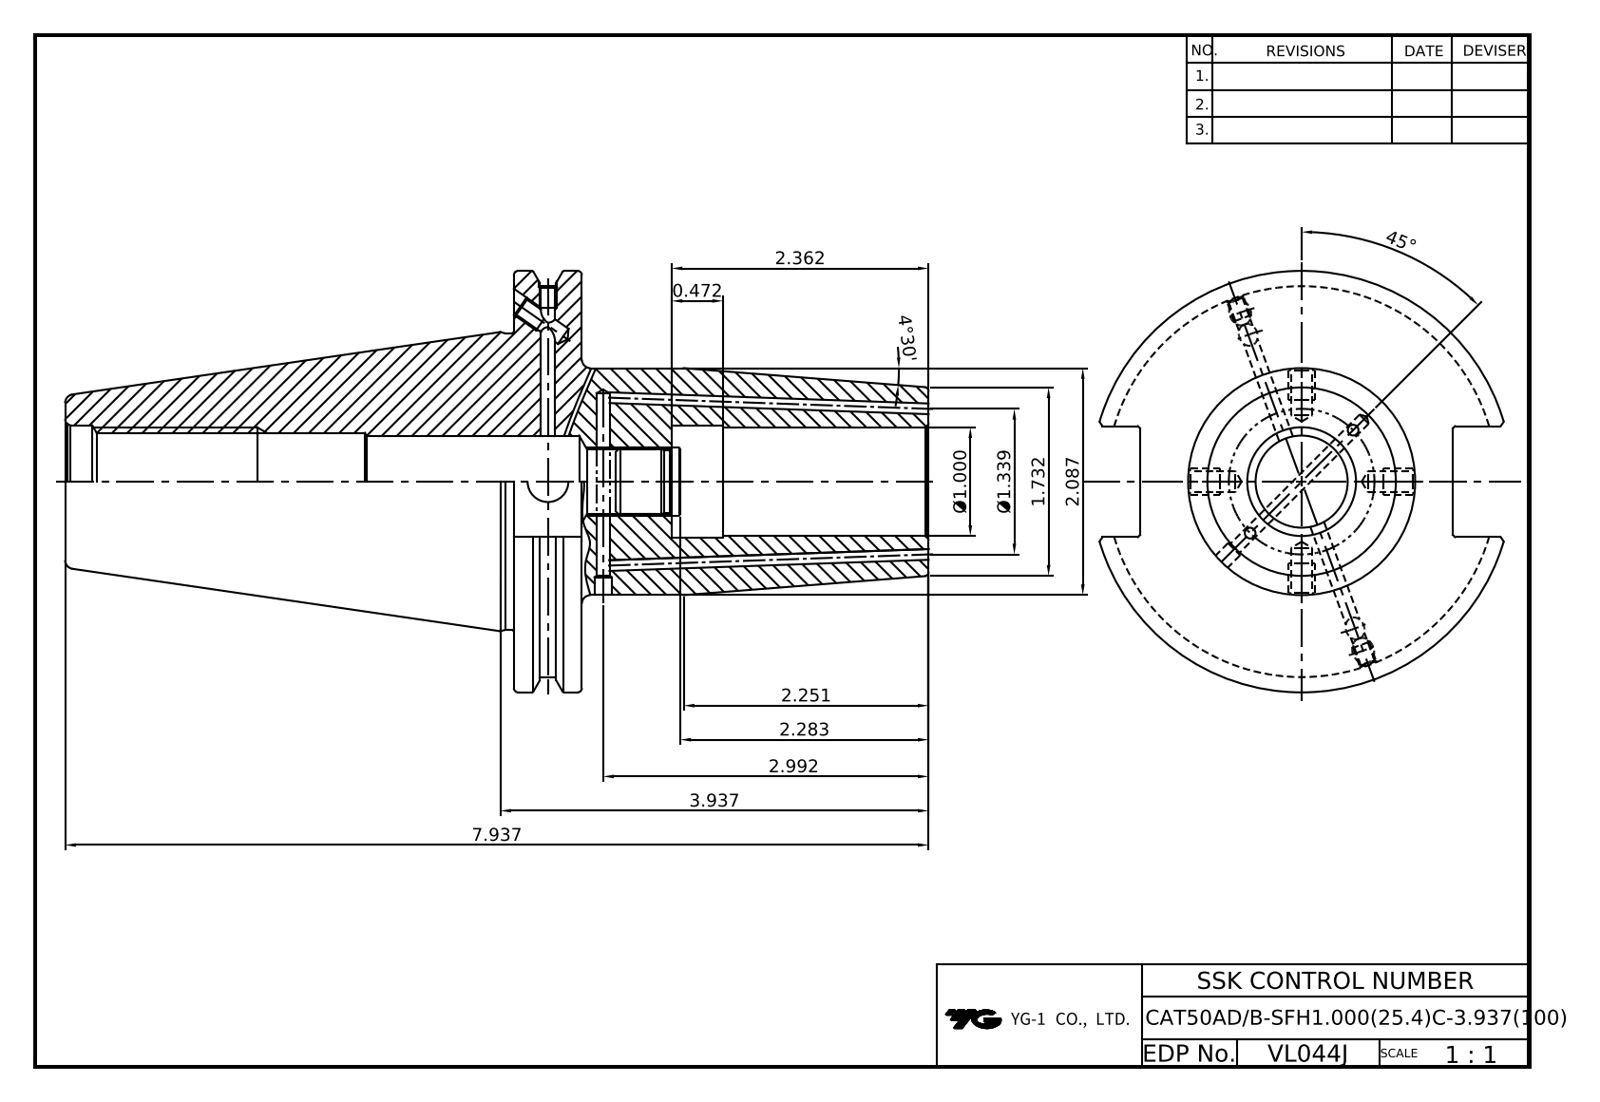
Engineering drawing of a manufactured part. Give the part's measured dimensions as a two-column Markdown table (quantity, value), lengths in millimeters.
| quantity | value |
| --- | --- |
| part name | LO-CAT50ADB-SFH25.4C-100 |
| STEP written by | Autodesk Inventor 2025 (AUTOMOTIVE_DESIGN) |
| units | millimeters |
| bodies | 1 solid, 88 faces (37 planar, 28 cylindrical, 23 other) |
| overall size | 201.6 × 98.42 × 94.69 |
| volume | 442 085 mm³ |
| surface area | 63 491 mm² |
| round holes (diameter × count) | 2.5 × 2, 3.24 × 2, 4.13 × 2, 4.2 × 2, 5 × 2, 9.53 × 1, 14.92 × 1, 21.97 × 1, 25.4 × 1, 26.2 × 1, 26.6 × 1 |
| round bosses / shafts (diameter × count) | 98.42 × 1, 91.29 × 1, 69.25 × 1, 53 × 1 |
| main face-to-face distances | 15.88, 96.83, 80.95, 104.77, 120.65, 201.6, 141.6, 36.83, 20.95, 60 |
